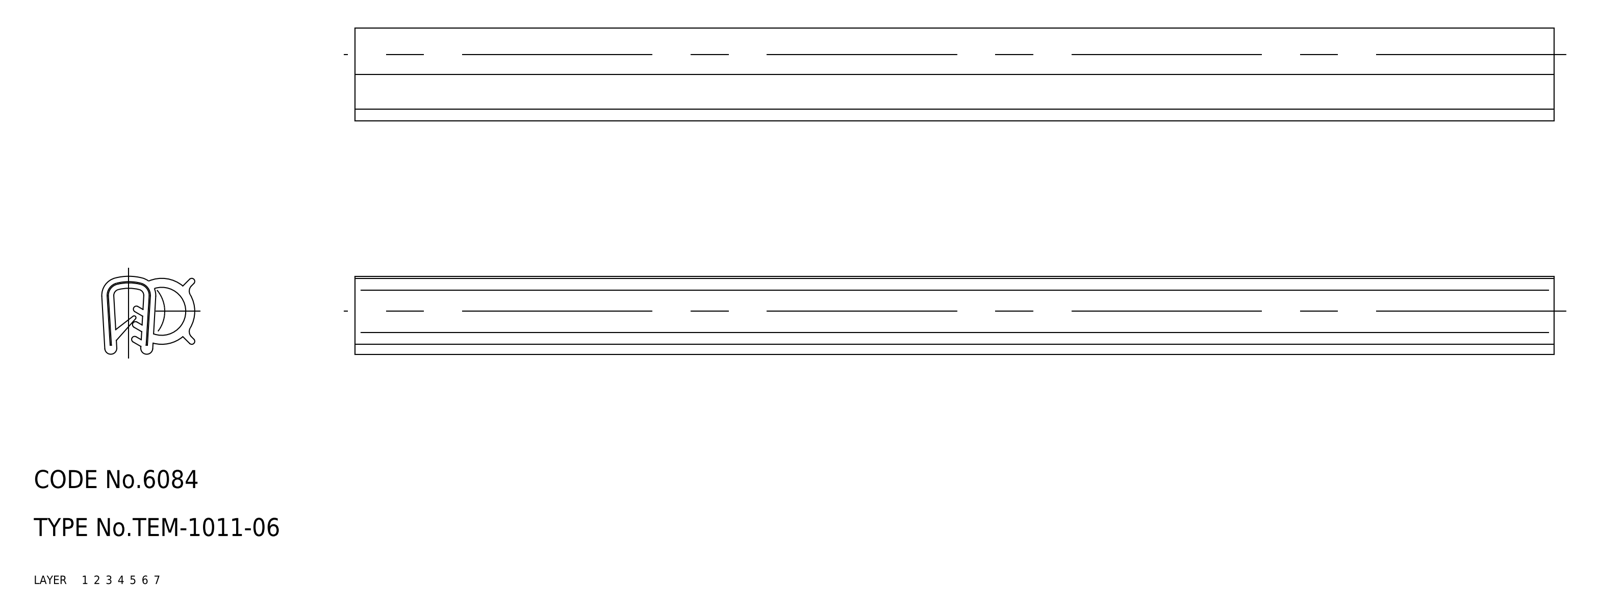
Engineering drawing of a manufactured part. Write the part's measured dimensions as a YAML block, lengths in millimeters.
part_name: "rubber foam; gasket; center core; TEM_1011_06_30024_36"
step_written_by: "CADfix (AUTOMOTIVE_DESIGN)"
units: millimeters
bodies: {solids: 3, faces: 72, planar: 0, cylindrical: 0, other: 72}
overall_size: [200, 15.5, 13]
volume: 19516
surface_area: 45668
